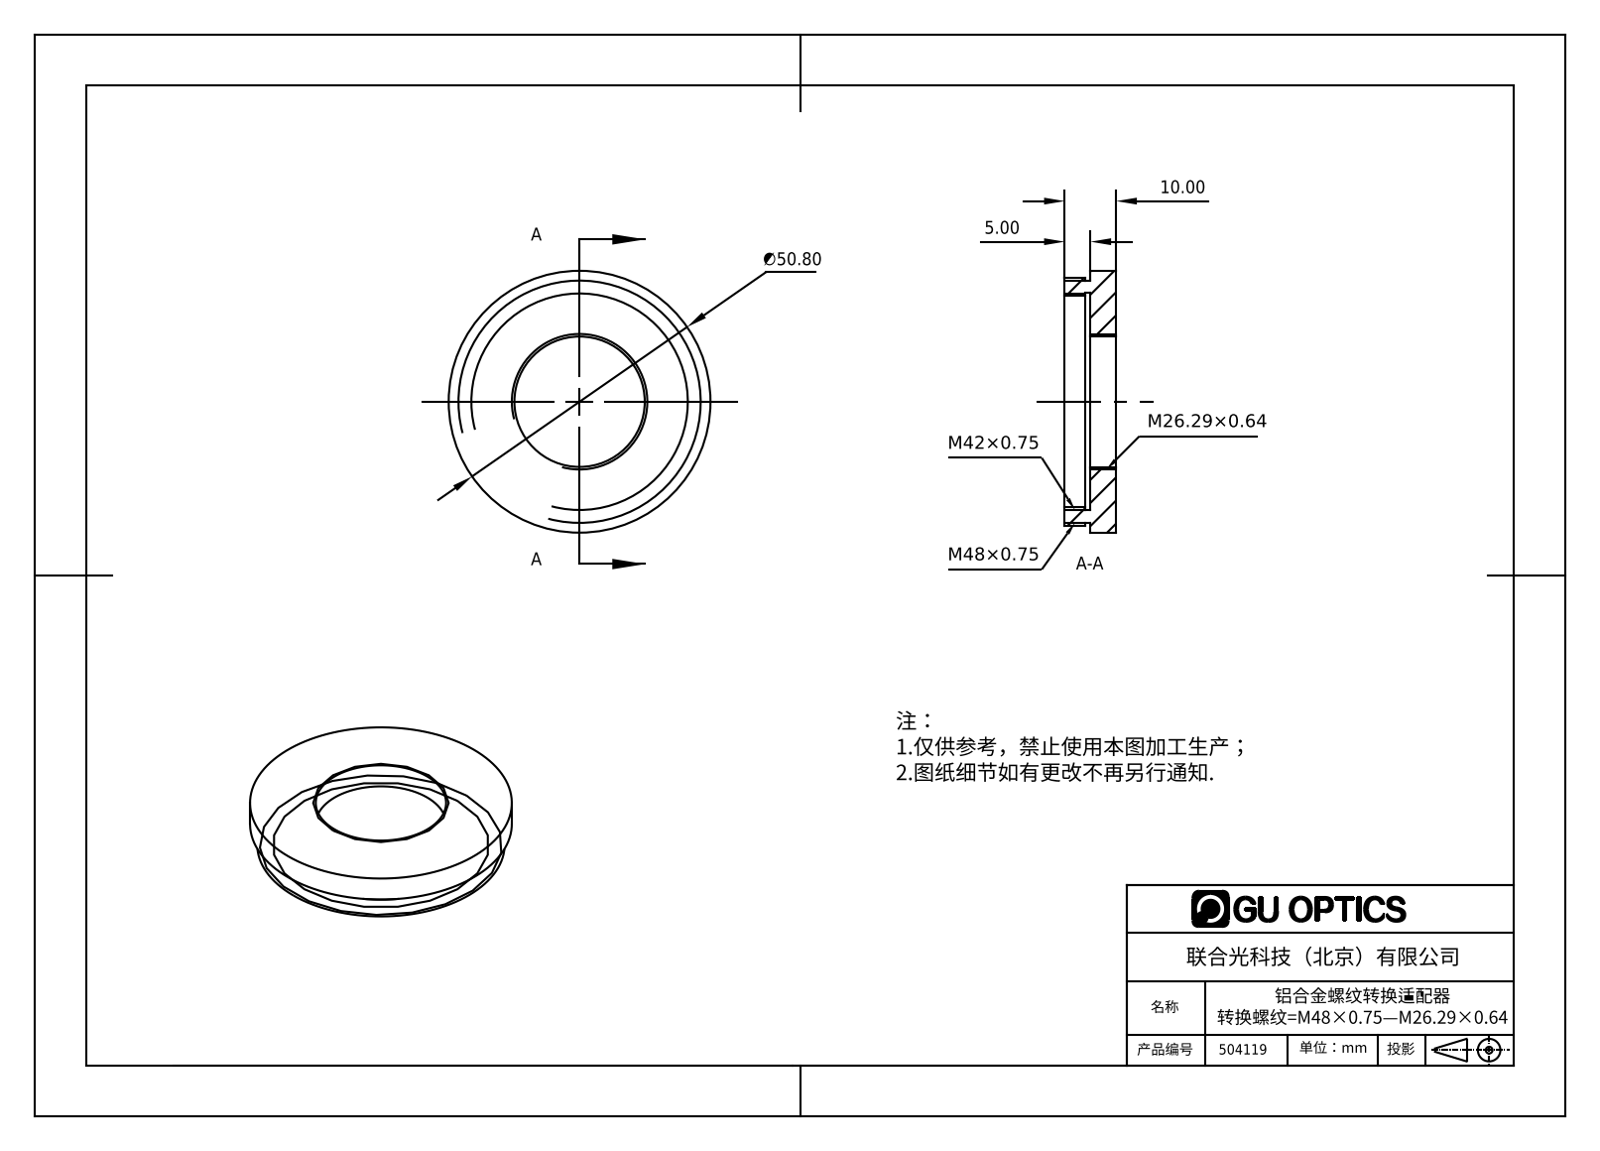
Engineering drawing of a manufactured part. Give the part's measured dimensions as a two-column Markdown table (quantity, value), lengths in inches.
| quantity | value |
| --- | --- |
| part name | 504119 |
| STEP written by | SolidWorks 2016 (AUTOMOTIVE_DESIGN) |
| units | inches |
| bodies | 1 solid, 18 faces (6 planar, 12 cylindrical, 0 other) |
| overall size | 2 × 2 × 0.394 |
| volume | 0.605 in³ |
| surface area | 9.221 in² |
| round holes (diameter × count) | 0.996 × 1, 1.614 × 1, 1.661 × 1 |
| round bosses / shafts (diameter × count) | 2 × 1, 1.89 × 1, 1.85 × 1 |
| main face-to-face distances | 0.197, 0.394, 0.157, 0.039, 0.236 |
